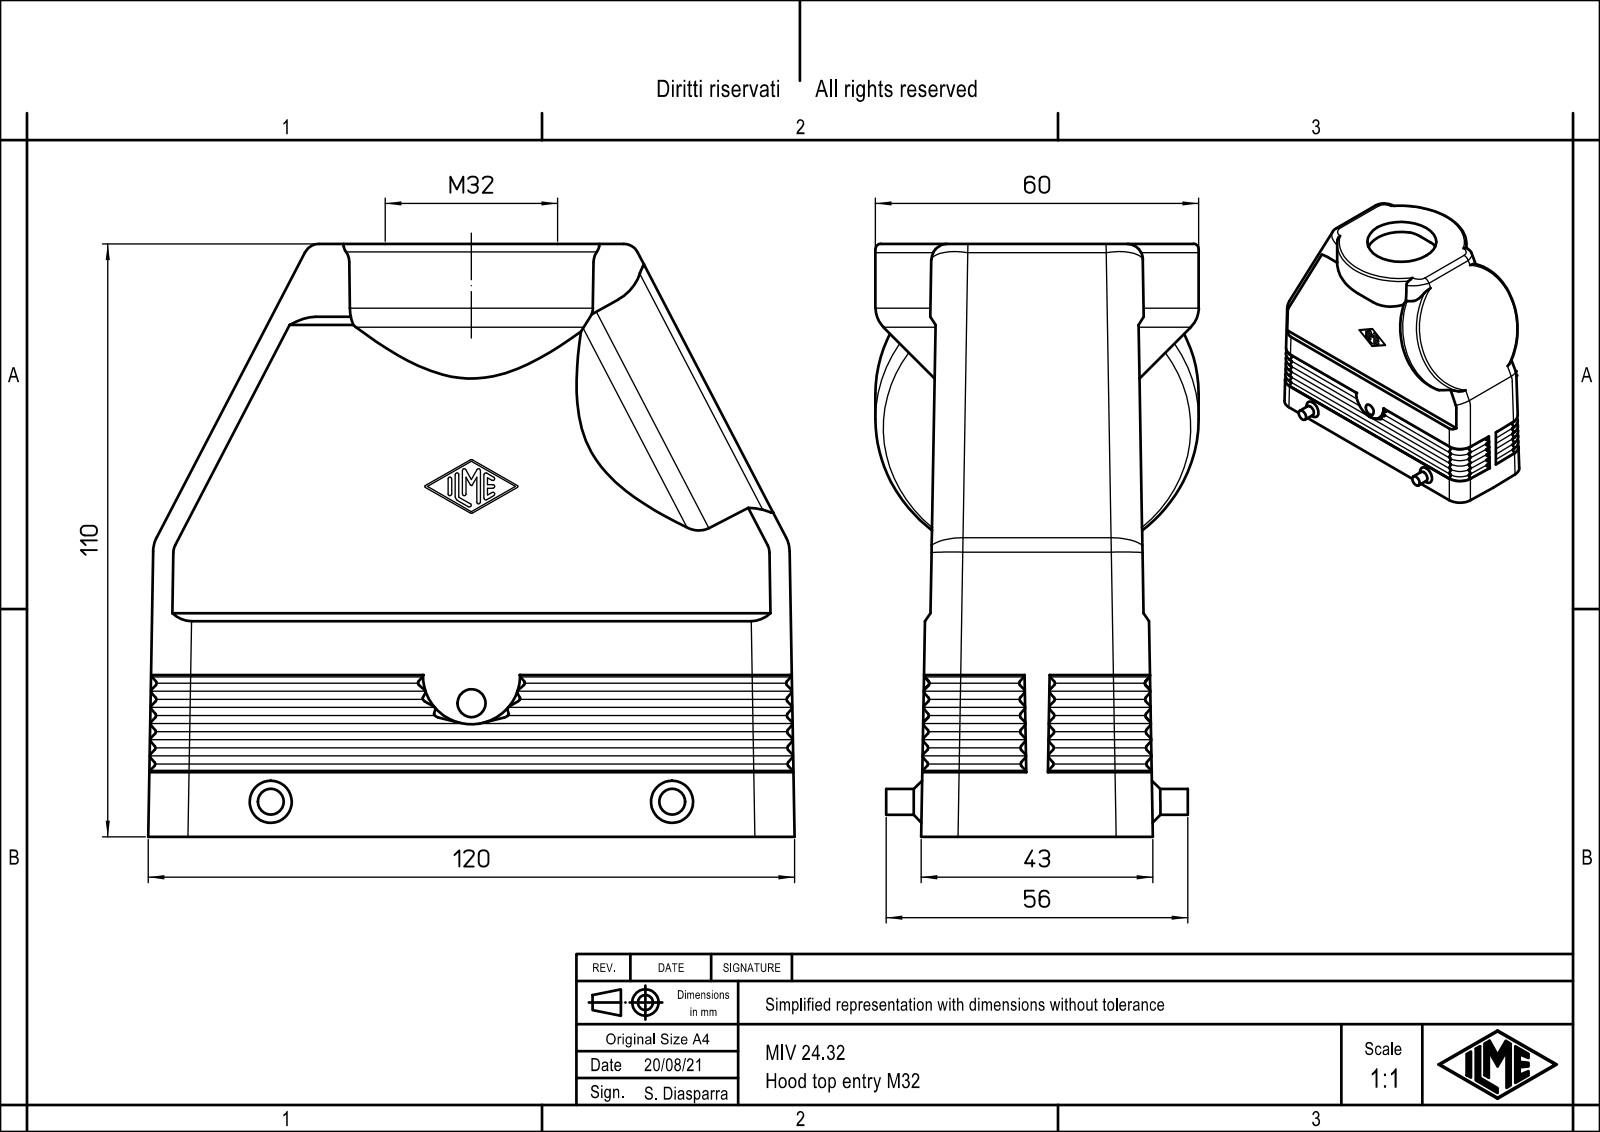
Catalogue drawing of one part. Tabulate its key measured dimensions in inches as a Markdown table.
| quantity | value |
| --- | --- |
| part name | MIV_24.32 |
| STEP written by | Creo Elements/Direct Modeling 20.1B 02-Apr-2019 (C) Parametric Technology GmbH (AUTOMOTIVE_DESIGN) |
| units | inches |
| bodies | 1 solid, 574 faces (234 planar, 171 cylindrical, 169 other) |
| overall size | 4.694 × 4.299 × 2.362 |
| volume | 7.113 in³ |
| surface area | 104.3 in² |
| round holes (diameter × count) | 0.138 × 4, 0.205 × 1, 1.26 × 1 |
| round bosses / shafts (diameter × count) | 0.189 × 2 |
| partial cylindrical surfaces (radius × count) | 0.02 × 78, 0.118 × 10, 0.276 × 8, 0.165 × 4, 1.181 × 2, 1.33 × 2, 0.039 × 1 |
| main face-to-face distances | 0.041, 0.042, 0.079, 0.22, 0.094, 0.157, 0.313, 0.205, 0.335, 0.236 |
| hole center spacings | 2.115, 1.063, 4.094, 4.23 |
